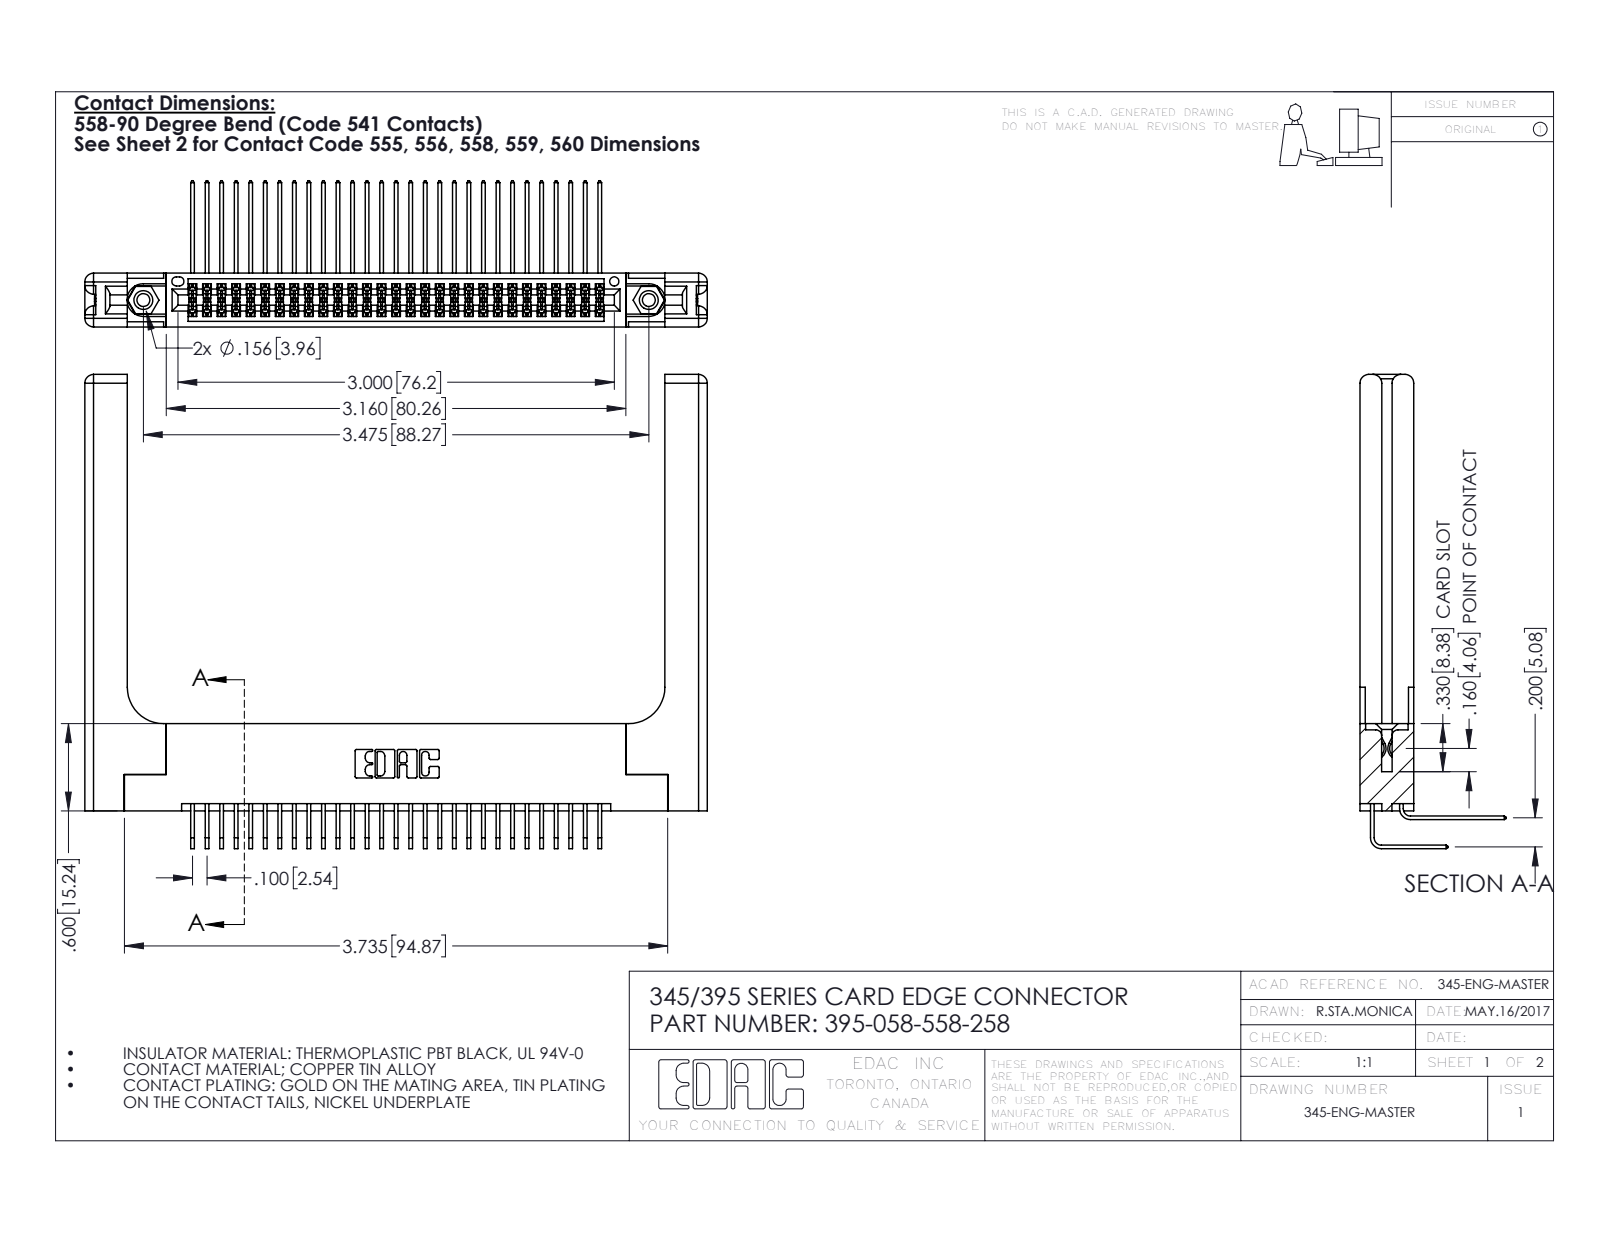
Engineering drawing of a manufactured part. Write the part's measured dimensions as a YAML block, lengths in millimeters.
part_name: "345-292-001_558 559 Tail - 1; 345-292-001_558 Tail - 2; 345-220-058_345-220-058; 395-058-558-258 (+2 more)"
step_written_by: "SolidWorks 2016 (CONFIG_CONTROL_DESIGN)"
units: millimeters
bodies: {solids: 63, faces: 3398, planar: 2258, cylindrical: 1080, other: 60}
overall_size: [108.7, 82.8, 25.5]
volume: 19250
surface_area: 22300
round_holes:
  - {diameter: 2.3, count: 2}
  - {diameter: 3.2, count: 2}
  - {diameter: 4, count: 2}
  - {diameter: 1.6, count: 1}
round_bosses_or_shafts:
  - {diameter: 3.9, count: 2}
partial_cylinders:
  - {radius: 0.2, count: 88}
  - {radius: 0.3, count: 22}
  - {radius: 1.5, count: 16}
  - {radius: 0.2, count: 6}
  - {radius: 0.8, count: 6}
  - {radius: 0.7, count: 3}
  - {radius: 0.4, count: 2}
  - {radius: 0.5, count: 2}
face_to_face_distances: [9.4, 1.8, 7.6, 5.1, 2.5, 6.9, 0.6, 5.7, 3.8, 3.8]
hole_center_spacings: [6.9, 82.3, 88.3]
